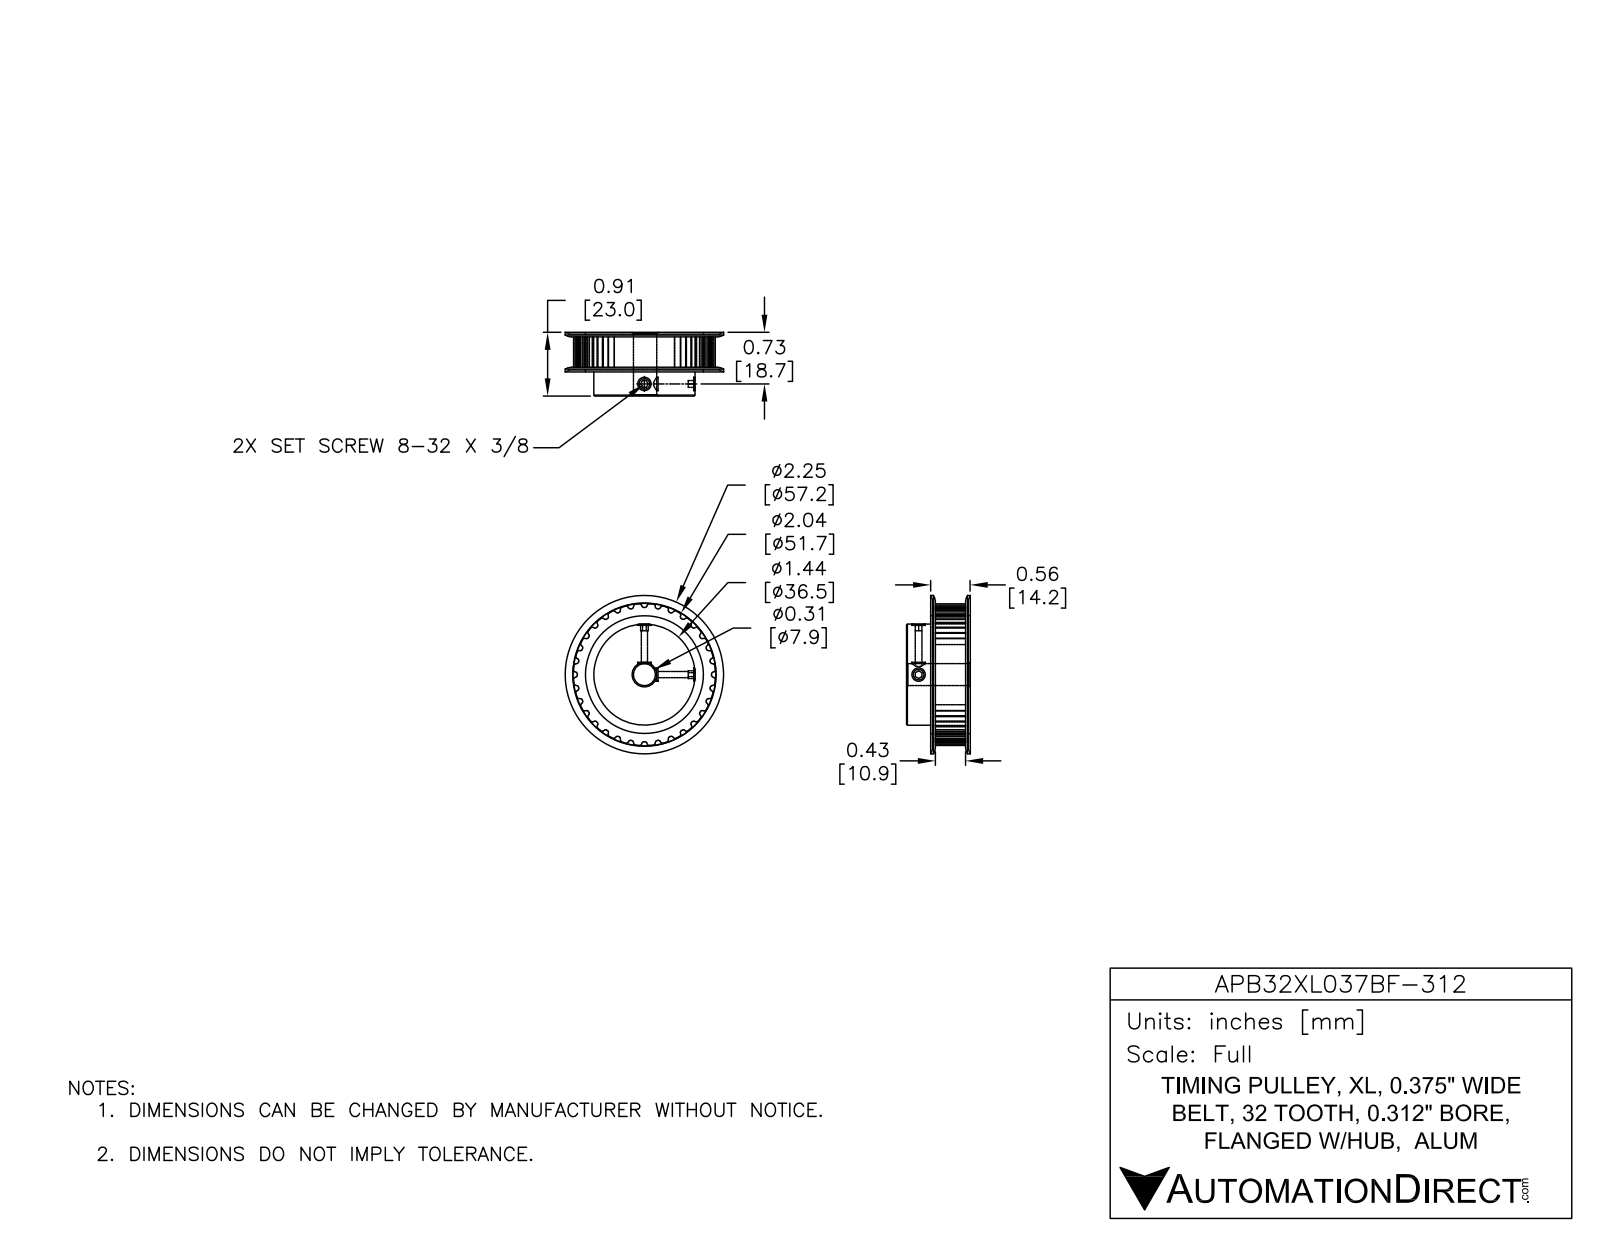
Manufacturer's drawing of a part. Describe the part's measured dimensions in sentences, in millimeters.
The part is named "APB32XL037BF-312". Its 3-D file was written by "SolidWorks 2014 (AUTOMOTIVE_DESIGN)". It is 1 solid with 314 faces: 102 planar, 190 cylindrical and 22 other. Overall it measures 57.2 by 57.2 by 23 millimeters. Its volume is 35 490 cubic millimeters and its surface area 10 700 square millimeters. Round holes: 2 of diameter 2.2, 1 of diameter 8. Round bosses or shafts: 1 of diameter 36.5. Partial cylindrical surfaces (rounded edges, fillets, slot ends): 128 of radius 0.4, 1 of radius 24.2. The main face-to-face distances are 12.6, 0.8, 13.4, 23, 22.2, 9.6, 51.2, 19.3, 11.7, 10.4.
